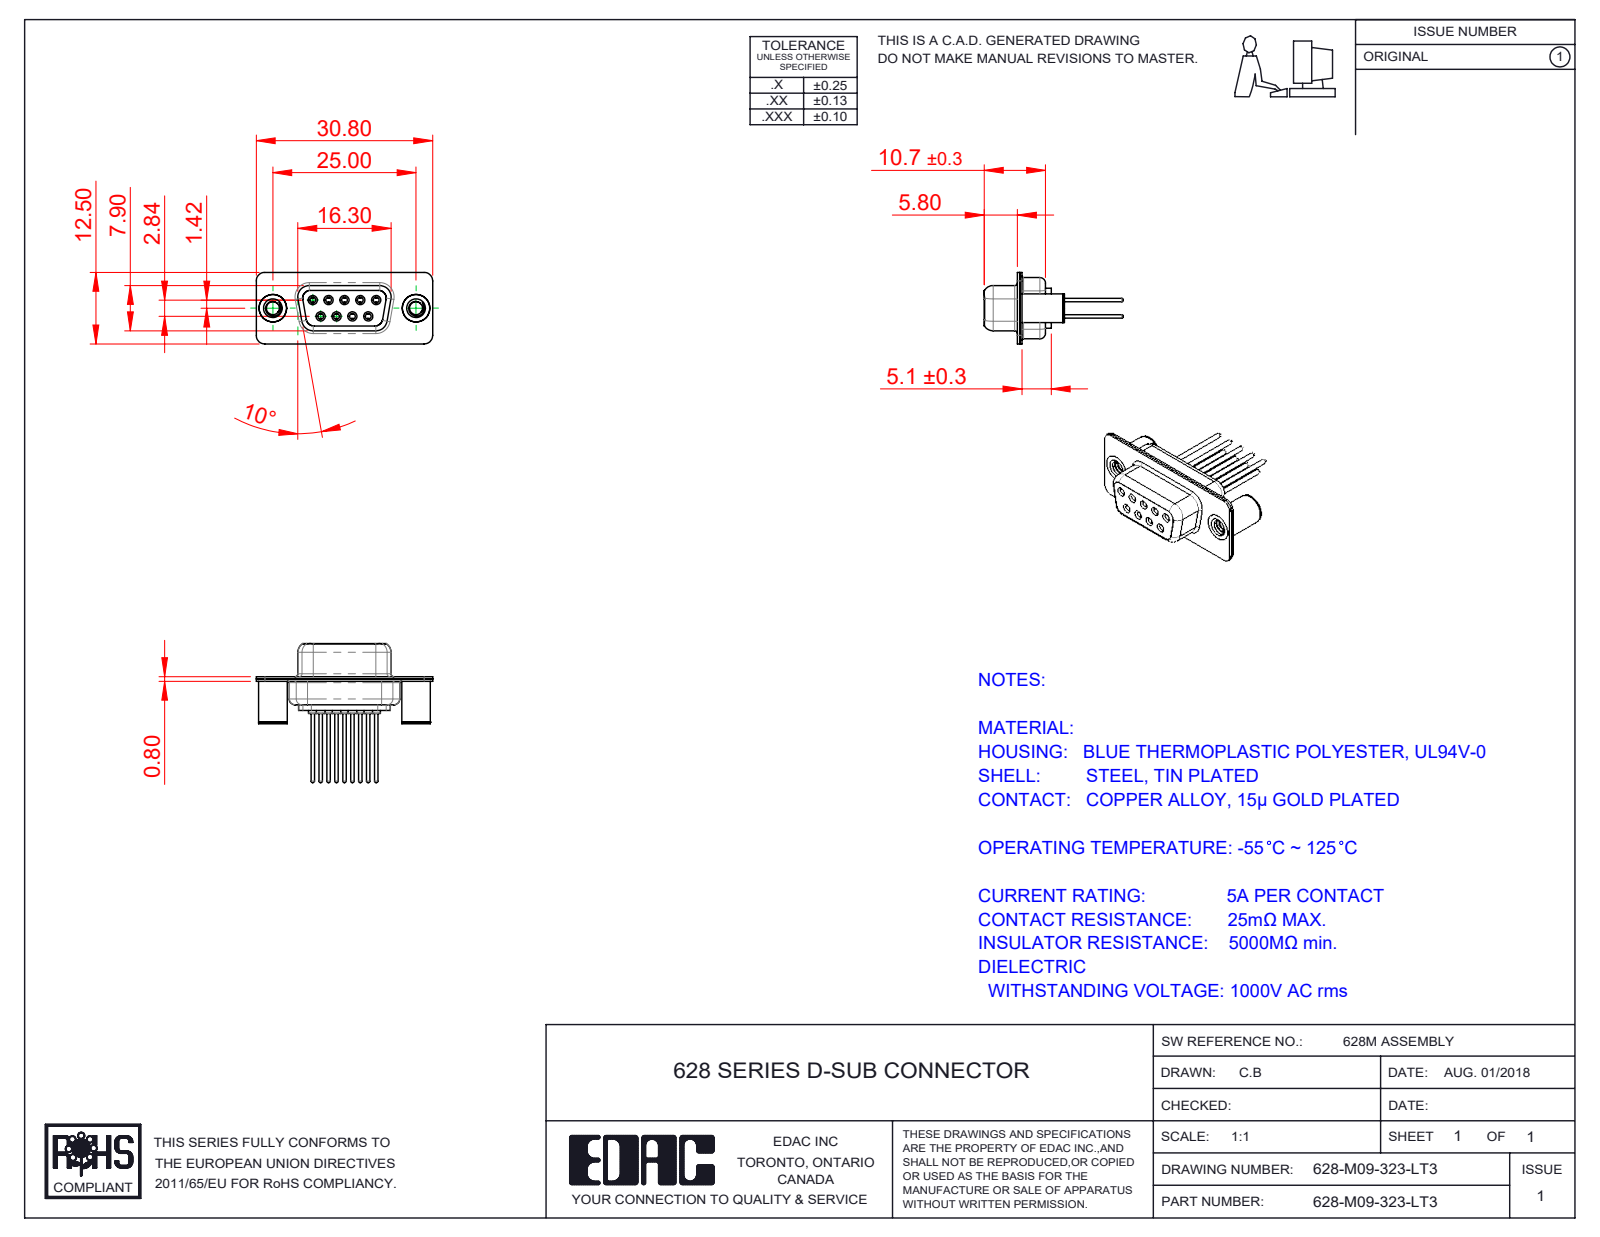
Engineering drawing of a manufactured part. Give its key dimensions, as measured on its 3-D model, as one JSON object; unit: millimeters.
{"part_name": "628M Shell Rear_09 Contacts; 628M Housing_09 Contacts; 628M Shell Front_09 Contacts; 628M Contact Row 2_23 (+3 more)", "step_written_by": "SolidWorks 2020 (CONFIG_CONTROL_DESIGN)", "units": "millimeters", "bodies": {"solids": 14, "faces": 808, "planar": 202, "cylindrical": 332, "other": 274}, "overall_size": [30.8, 24.27, 12.5], "volume_mm3": 1842, "surface_area_mm2": 4794, "round_holes": [[1, 9], [1.1, 9], [1.7, 9], [1.8, 9], [2, 9], [2.26, 2], [3.26, 2], [4, 2], [4.8, 2]], "round_bosses_or_shafts": [[2.2, 9], [1.6, 9], [1.5, 9], [0.6, 9], [5, 2], [4.9, 2]], "partial_cylinders_radius": [[1.5, 16], [2, 12], [1.35, 8], [1.6, 8], [0.25, 4], [0.5, 4], [0.6, 4], [0.65, 4]], "face_to_face_distances": [0.4, 1.4, 0.45, 8.45, 0.8, 1.8, 8.9, 1, 6.2, 7.05], "hole_center_spacings": [3.16, 2.77, 5.54, 5.03, 5.04, 8.31, 7.1, 7.48]}
